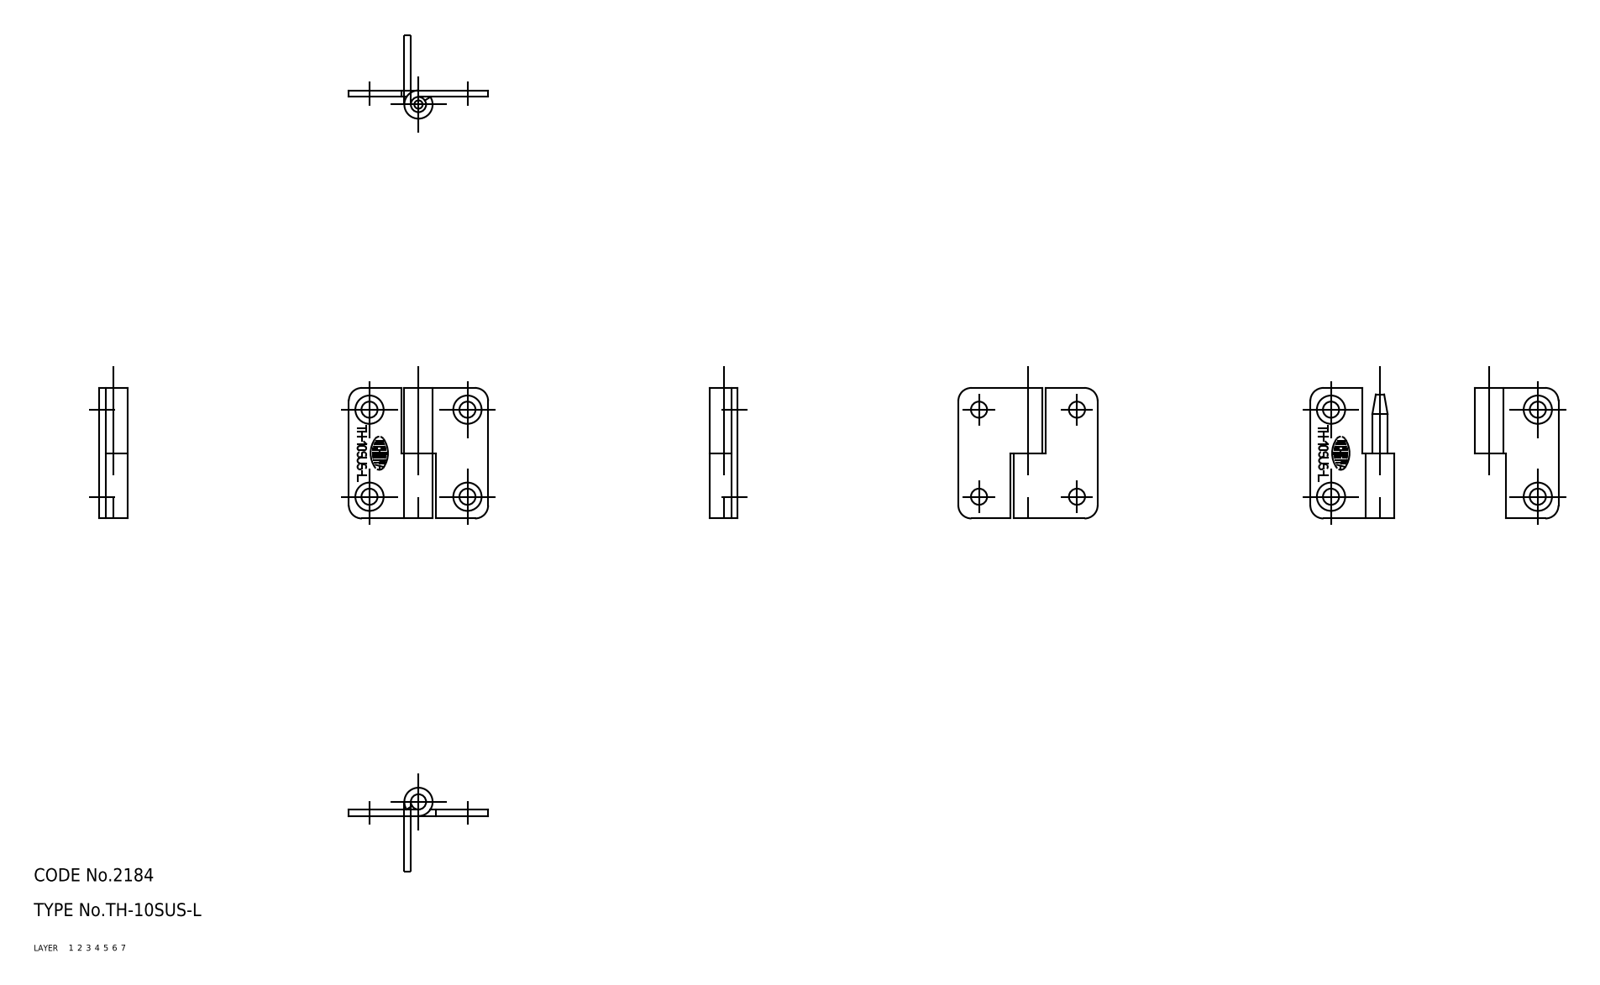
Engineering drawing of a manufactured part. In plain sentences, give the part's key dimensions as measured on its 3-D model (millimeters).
The part is named "shaft; hinge piece_B; hinge piece_A; TH_10SUS_L_31932_36". Its 3-D file was written by "CADfix (AUTOMOTIVE_DESIGN)". It is 3 solids with 46 faces: 0 planar, 0 cylindrical and 46 other. Overall it measures 32 by 30 by 6.5 millimeters. Its volume is 1 977 cubic millimeters and its surface area 3 072 square millimeters.
